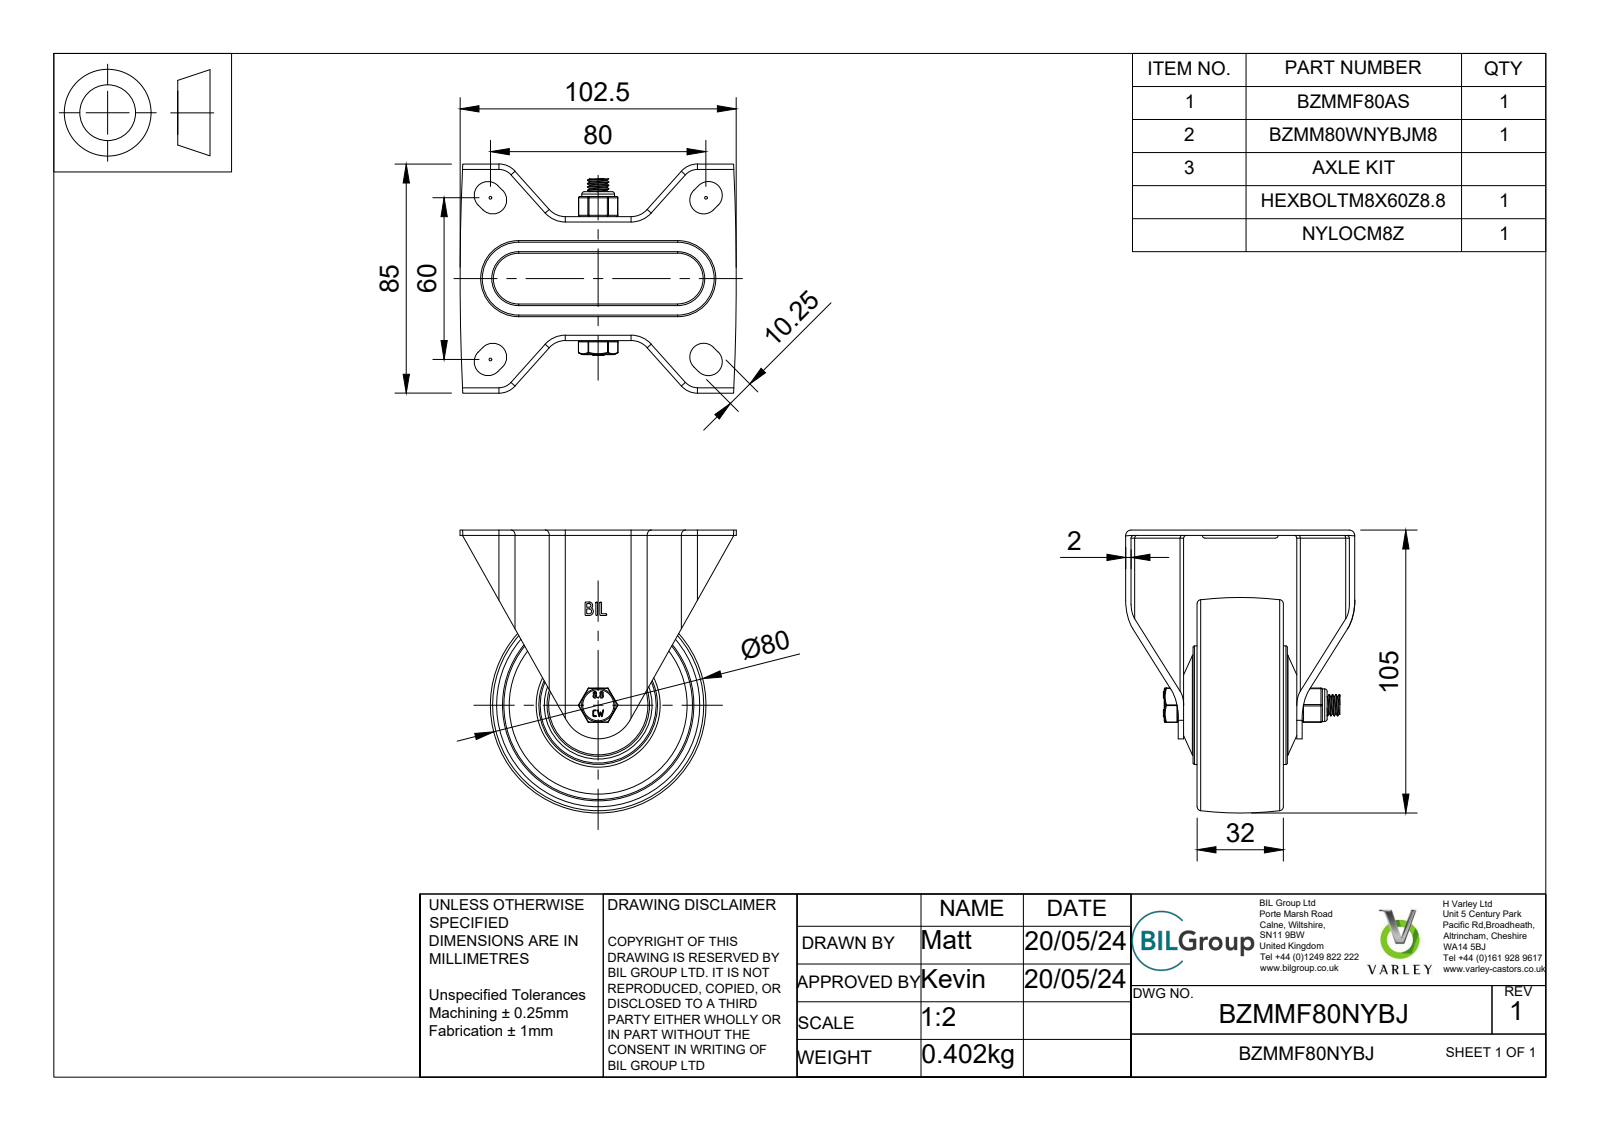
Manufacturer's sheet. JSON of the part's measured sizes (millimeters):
{"part_name": "BZMMF80NYBJ v4; BZMM80WNYBJM8 v1; BZMM80WNYBJ; NYLON WHEEL (+7 more)", "step_written_by": "Autodesk Translation Framework v13.14.0.145 (AUTOMOTIVE_DESIGN)", "units": "millimeters", "bodies": {"solids": 20, "faces": 781, "planar": 280, "cylindrical": 218, "other": 283}, "overall_size": [105, 102.5, 85], "volume_mm3": 122567, "surface_area_mm2": 87654, "round_holes": [[0.66, 2], [8, 1], [8.2, 1], [8.25, 1], [8.6, 1], [15, 1], [20, 1], [22.5, 1], [25, 1], [30, 1], [31, 1], [32, 1]], "round_bosses_or_shafts": [[44, 1], [38, 1], [30.5, 1], [28, 1], [23, 1], [19, 1], [18, 1], [14.9, 1]], "partial_cylinders_radius": [[0.5, 18], [0.25, 12], [1, 12], [2, 8], [4, 8], [5.12, 8], [8, 8], [0.33, 4]], "face_to_face_distances": [2, 26, 18, 20, 44, 24, 5.16, 13, 6, 46], "hole_center_spacings": [4.65, 2.49]}
